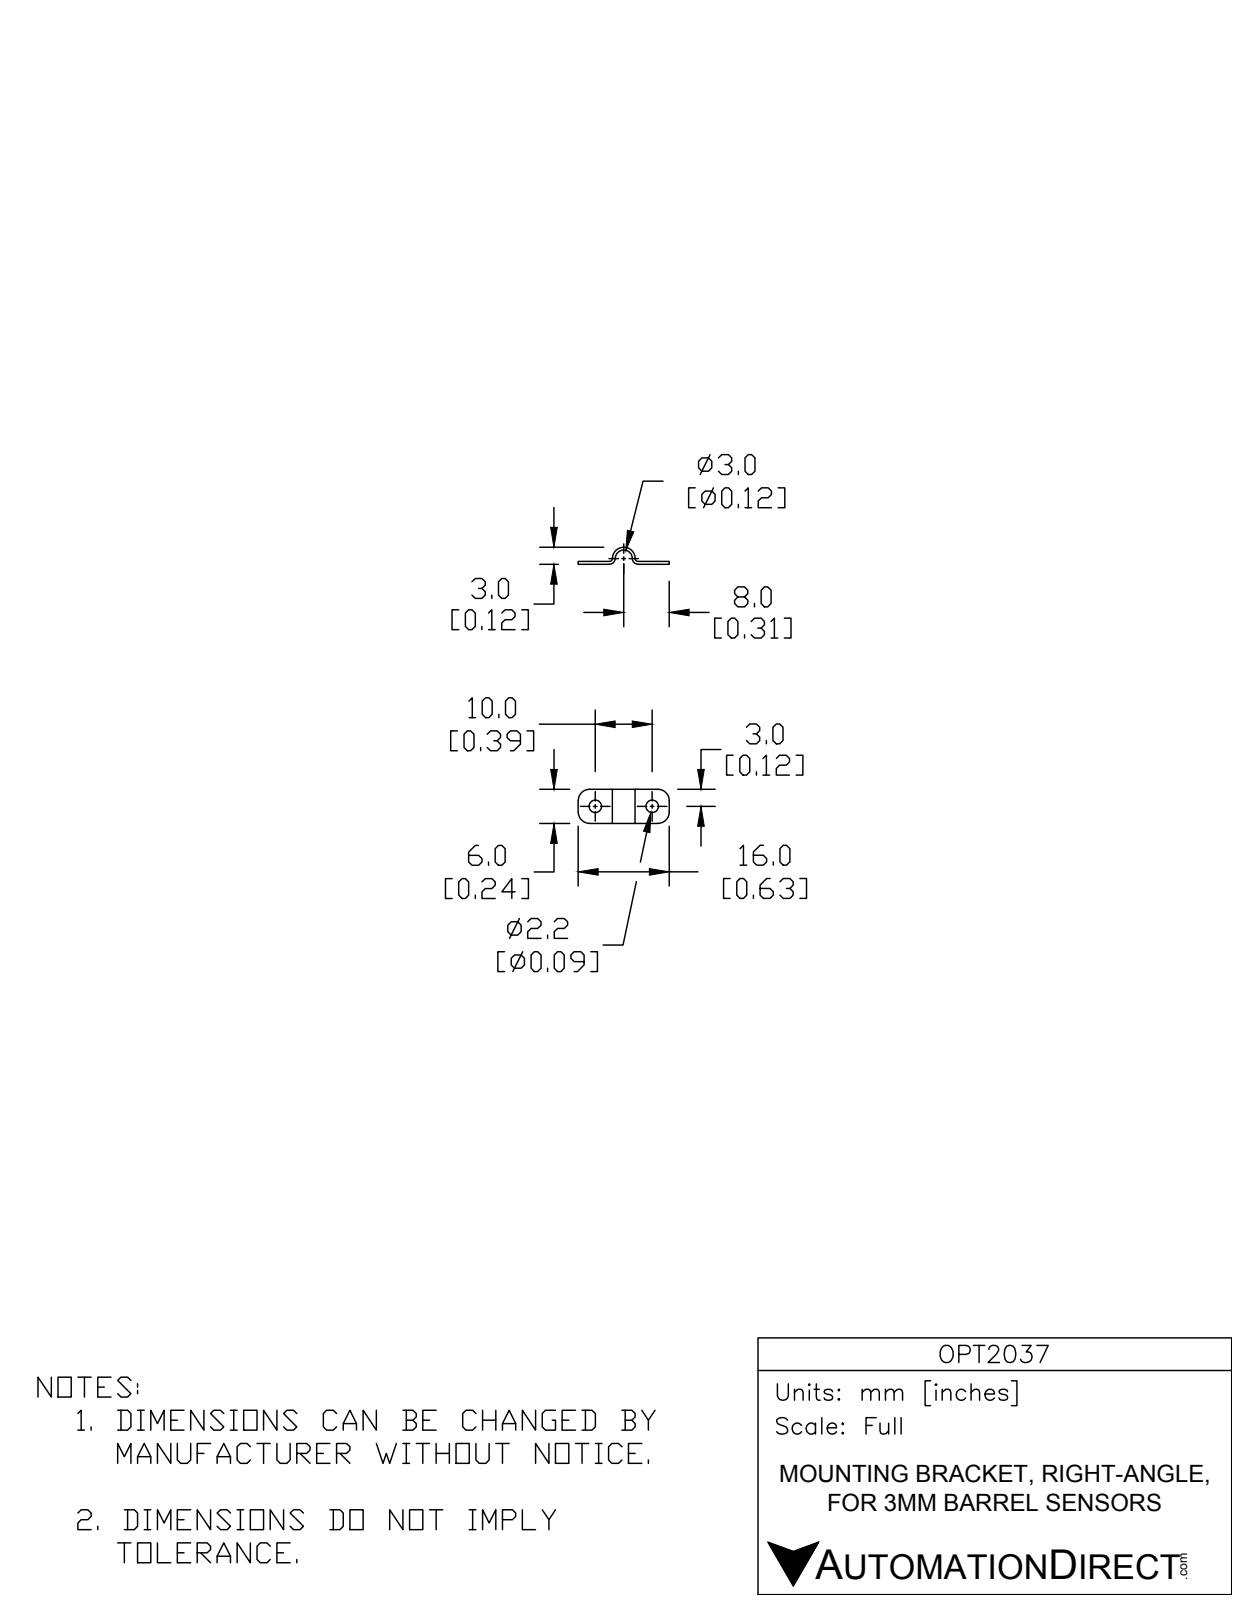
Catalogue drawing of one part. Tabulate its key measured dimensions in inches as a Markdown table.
| quantity | value |
| --- | --- |
| STEP written by | Solid Edge (CONFIG_CONTROL_DESIGN) |
| units | inches |
| bodies | 1 solid, 20 faces (8 planar, 12 cylindrical, 0 other) |
| overall size | 0.63 × 0.236 × 0.118 |
| volume | 0.003 in³ |
| surface area | 0.363 in² |
| round holes (diameter × count) | 0.087 × 2 |
| partial cylindrical surfaces (radius × count) | 0.079 × 5, 0.02 × 2, 0.039 × 2, 0.059 × 1 |
| main face-to-face distances | 0.02, 0.236, 0.63 |
| hole center spacings | 0.394 |
